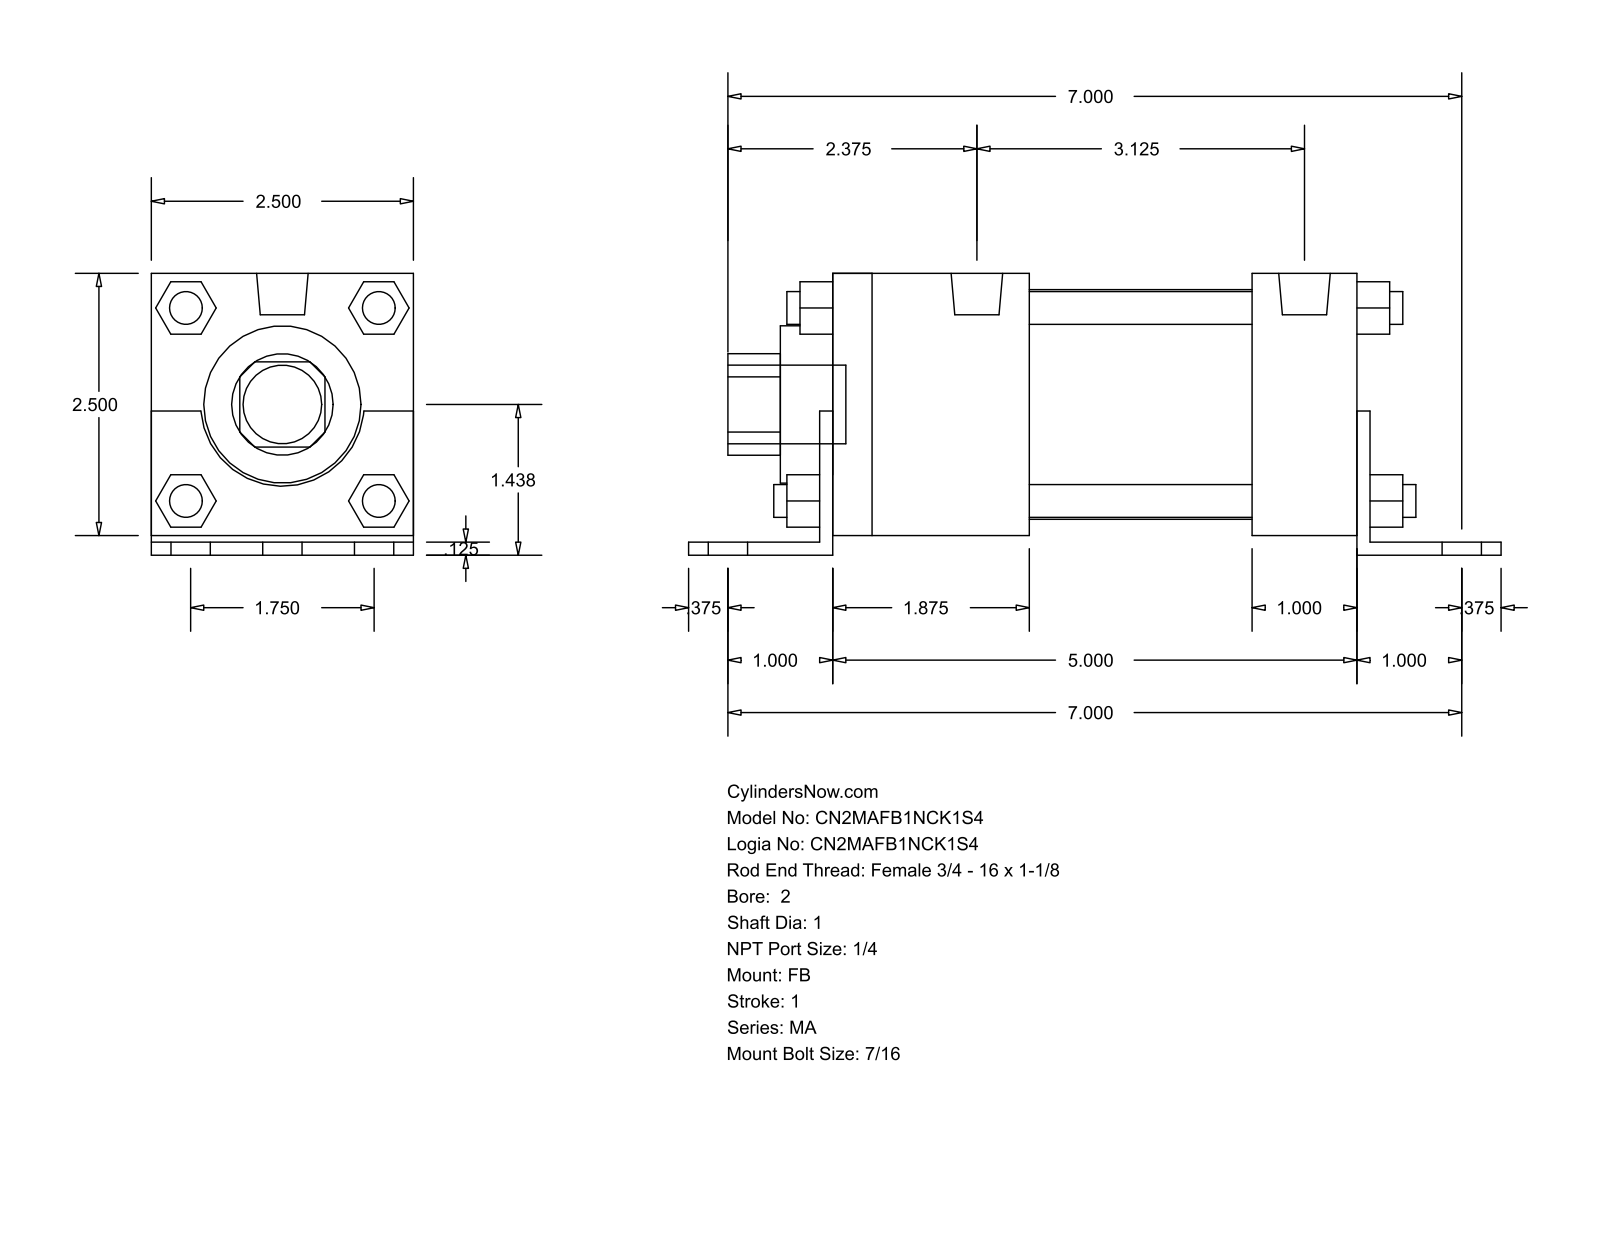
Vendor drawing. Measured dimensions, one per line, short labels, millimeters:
name: MA_FB__0200_1
written by: GSSL Pune (CONFIG_CONTROL_DESIGN)
unit: mm
bodies: 0 solids, 140 faces (105 planar, 35 cylindrical, 0 other)
size: 196.85 × 68.26 × 63.5
holes: 1× ⌀25.4, 1× ⌀38.1, 1× ⌀55.63
bosses: 8× ⌀7.94, 6× ⌀11.11, 2× ⌀12.49, 1× ⌀19.05
rounds: 1× R12.29, 1× R19.81
face distances: 63.5, 3.17, 4.76, 68.26, 1.59, 65.09, 130.17, 12.7, 127, 25.4
